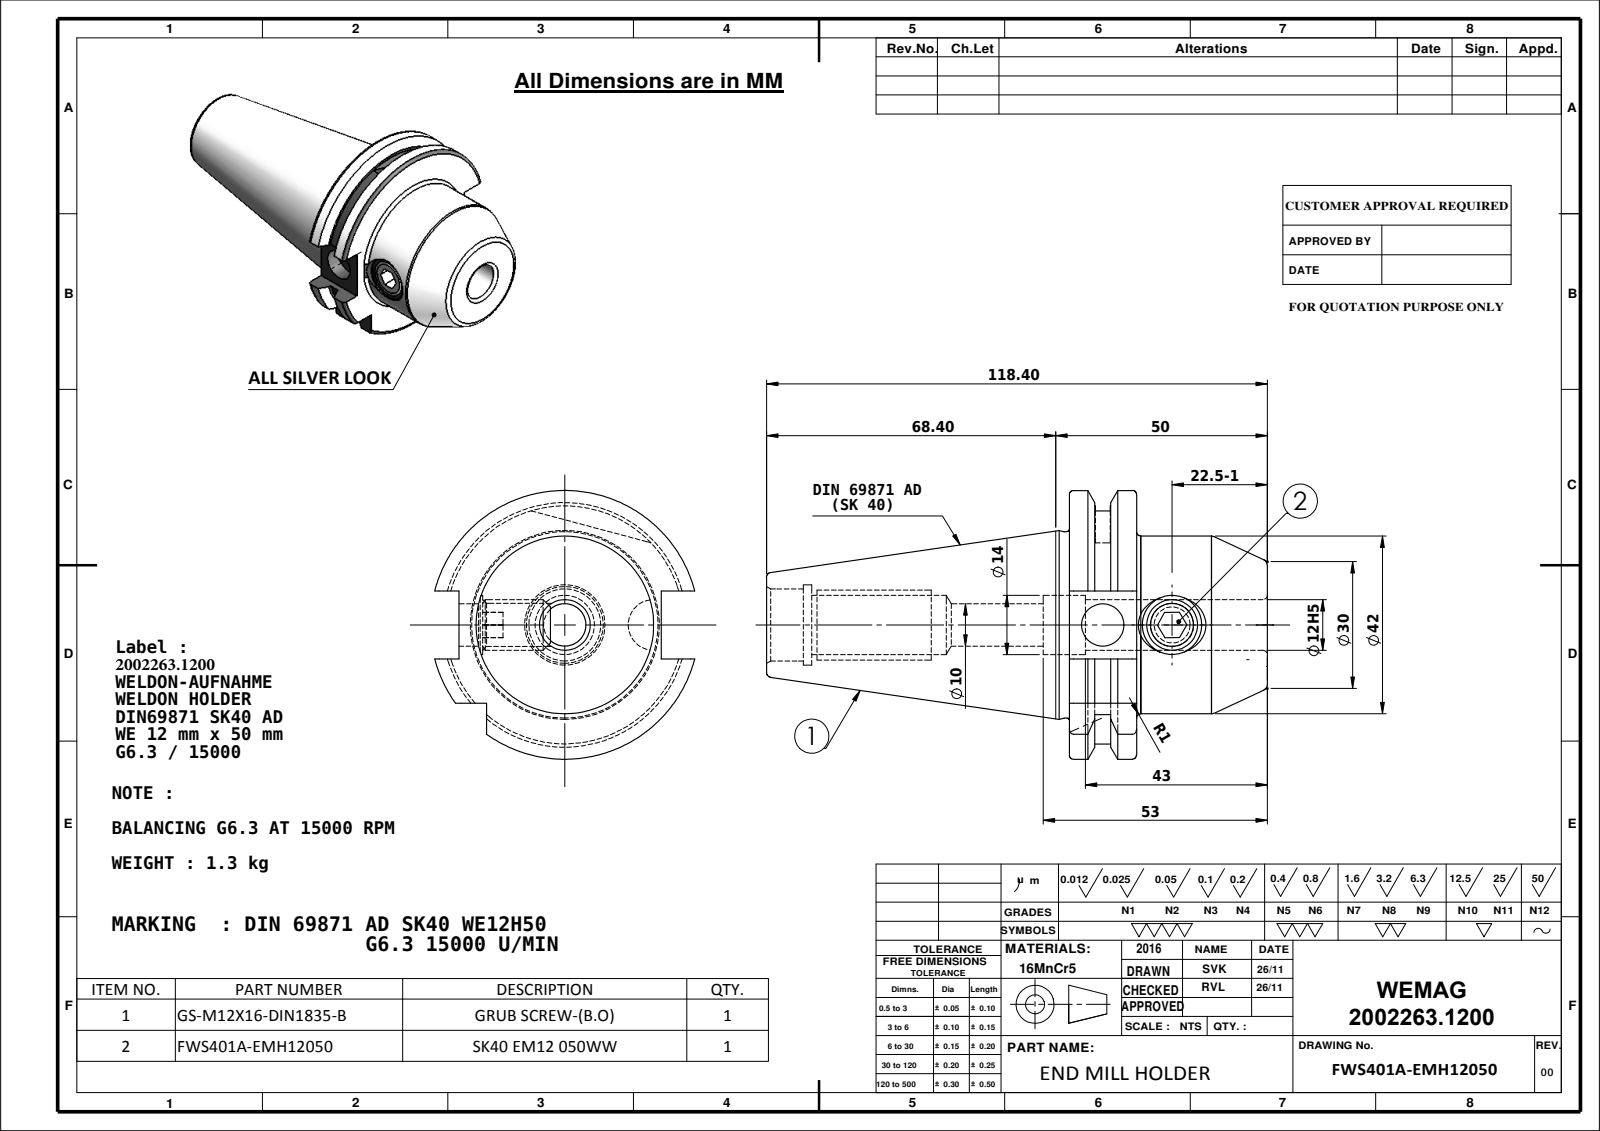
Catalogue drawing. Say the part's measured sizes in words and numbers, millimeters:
The part is named "91406-WE112050; SK40 EM 12 050 WW; M12X16._ISO 4026 - M12 x 12-N". Its 3-D file was written by "SolidWorks 2009 (CONFIG_CONTROL_DESIGN)". It is 2 solids with 124 faces: 36 planar, 36 cylindrical and 52 other. Overall it measures 118.4 by 63.55 by 61.48 millimeters. Its volume is 135 496 cubic millimeters and its surface area 26 215 square millimeters. Round holes: 2 of diameter 10, 2 of diameter 14, 1 of diameter 10.2, 1 of diameter 12, 1 of diameter 17, 1 of diameter 19. Round bosses or shafts: 1 of diameter 44.05, 1 of diameter 42, 1 of diameter 12. Partial cylindrical surfaces (rounded edges, fillets, slot ends): 1 of radius 28.12, 1 of radius 31.77. The main face-to-face distances are 15.9, 46.8, 30.9, 16.1, 47.8, 71.6, 87.5, 118.4, 10.7, 60.9. The hole center spacings are 16.4.
